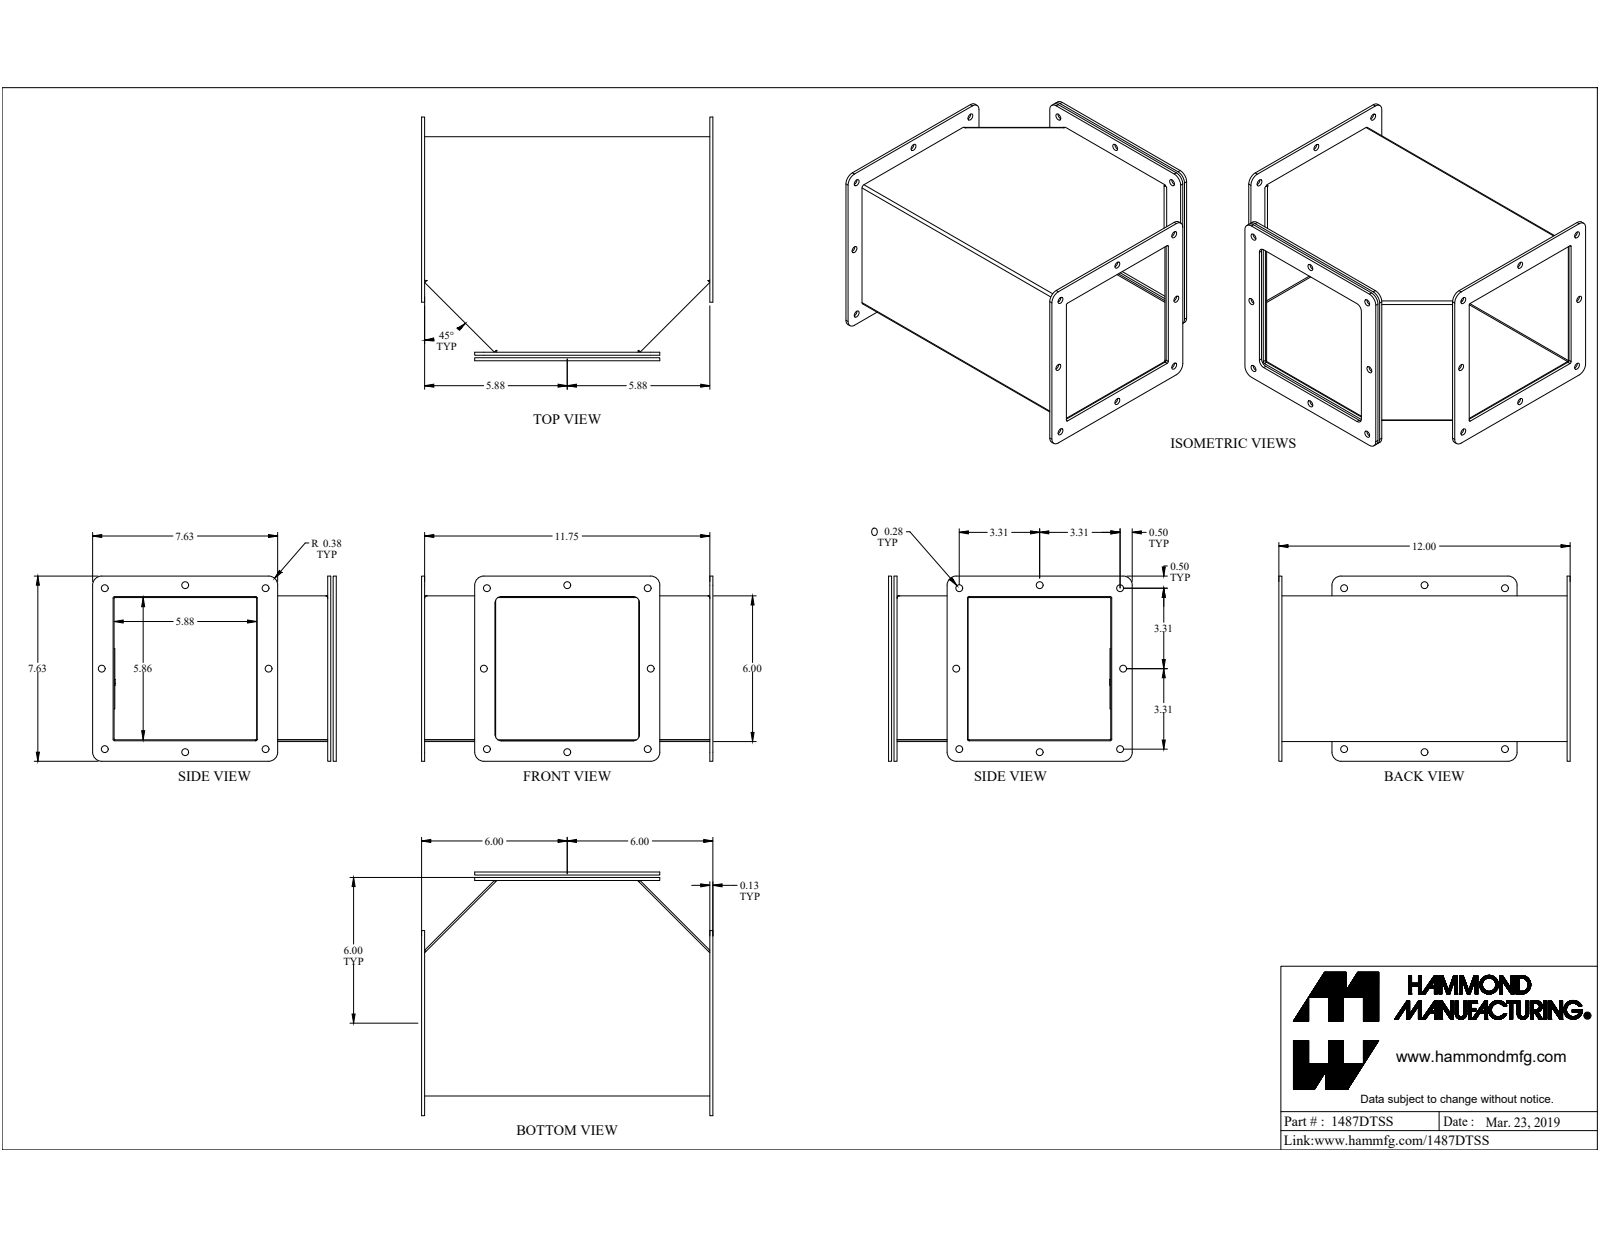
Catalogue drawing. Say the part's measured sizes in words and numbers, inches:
The part is named "1487DTSS". Its 3-D file was written by "SolidWorks 2019 (CONFIG_CONTROL_DESIGN)". It is 9 solids with 312 faces: 187 planar, 98 cylindrical and 27 other. Overall it measures 12 by 10.383 by 7.625 inches. Its volume is 33.63 cubic inches and its surface area 850.6 square inches. Round holes: 16 of diameter 0.281, 1 of diameter 0.196, 1 of diameter 0.258, 1 of diameter 0.35. Round bosses or shafts: 1 of diameter 0.5, 1 of diameter 0.25. Partial cylindrical surfaces (rounded edges, fillets, slot ends): 12 of radius 0.375, 8 of radius 0.063, 6 of radius 0.02, 4 of radius 0.036, 4 of radius 0.108, 4 of radius 0.25. The main face-to-face distances are 0.072, 5.928, 5.856, 6, 0.125, 11.875, 11.75, 0.225, 0.125, 0.35. The hole center spacings are 7.519, 3.315, 4.861, 6.625, 9.369, 6.875, 3.315, 4.861.
